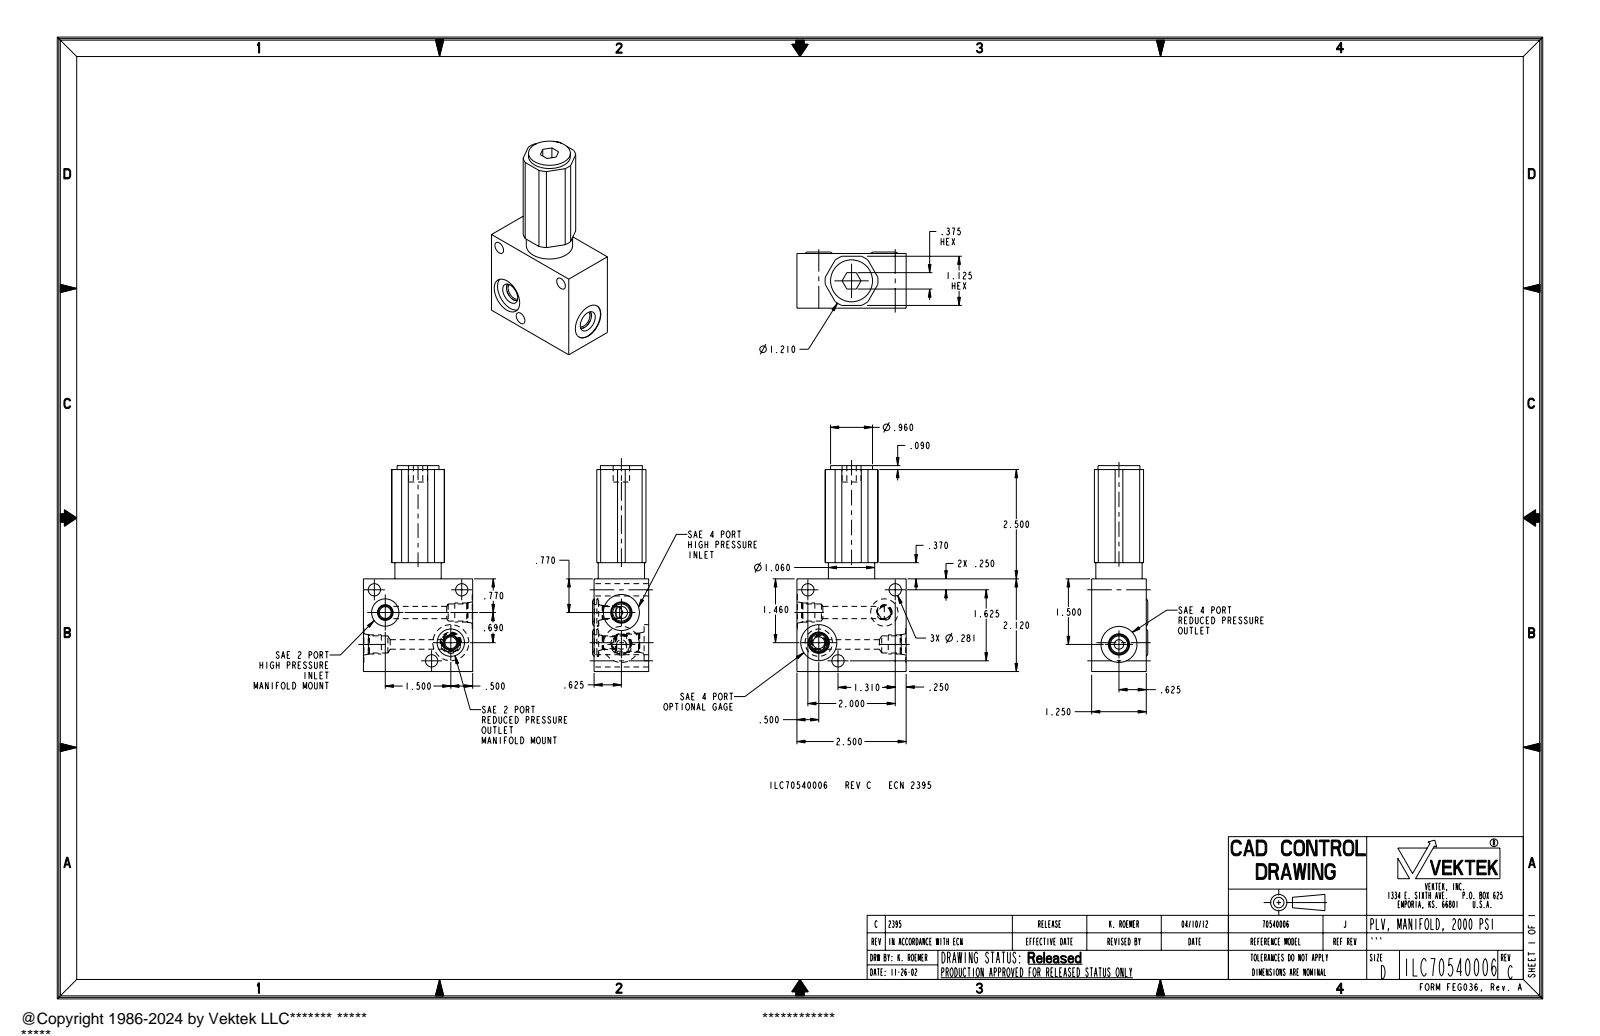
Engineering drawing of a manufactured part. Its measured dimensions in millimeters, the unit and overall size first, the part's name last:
Units: millimetres
Overall size (bounding box): 119.6 × 63.5 × 32.6
Round holes (diameter × count): ⌀7.1 ×4, ⌀10 ×3, ⌀21 ×3, ⌀6.9 ×2, ⌀15.9 ×2, ⌀5.5 ×1
Round bosses / shafts (diameter × count): ⌀11.1 ×3, ⌀7.9 ×2, ⌀26.9 ×1, ⌀24.4 ×1
Partial cylindrical surfaces — rounded edges, fillets, slot ends (radius × count): R15.4 ×1
Main face-to-face distances: 31.8, 28.6, 63.5, 53.8, 1.6, 30.2, 63.2, 2.7, 29.1, 1.1
Hole centre spacings: 14.7, 15.4, 18.5, 31.4, 38.9, 41.9, 44.9, 46.4
Volume: 139 600 mm³ · Surface area: 28 120 mm²
Bodies: 1 solid, 118 faces (33 planar, 54 cylindrical, 31 other)
Part name (STEP PRODUCT): ILC70540006
STEP written by: PRO/ENGINEER BY PARAMETRIC TECHNOLOGY CORPORATION, 2007460 (AUTOMOTIVE_DESIGN_CC2)
